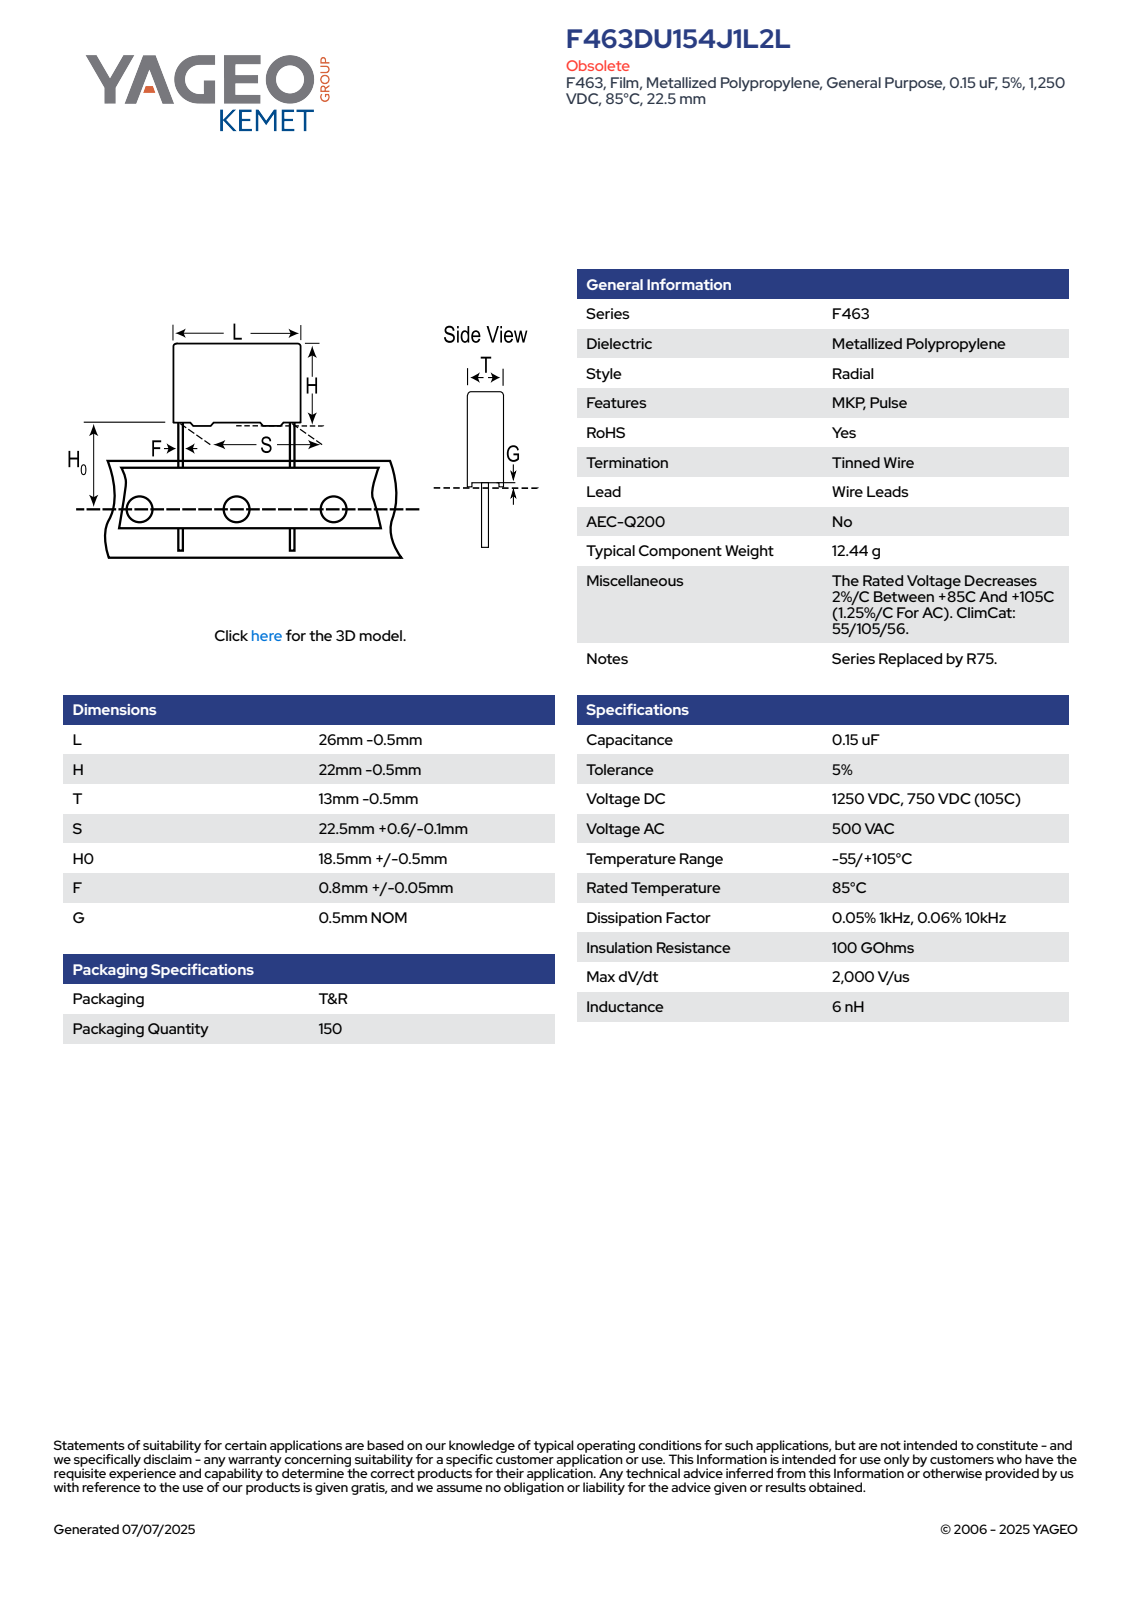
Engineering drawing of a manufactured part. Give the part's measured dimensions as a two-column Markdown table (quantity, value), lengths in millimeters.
| quantity | value |
| --- | --- |
| part name | CFR_RBG_26X22X13_L25.5H21.5T12.5S22.5H019F0.85G0.5 |
| STEP written by | SolidWorks 2014 (AUTOMOTIVE_DESIGN) |
| units | millimeters |
| bodies | 4 solids, 89 faces (81 planar, 8 cylindrical, 0 other) |
| overall size | 40.5 × 25.5 × 12.51 |
| volume | 6 718 mm³ |
| surface area | 2 410 mm² |
| round bosses / shafts (diameter × count) | 0.85 × 2 |
| partial cylindrical surfaces (radius × count) | 0.5 × 4 |
| main face-to-face distances | 12.5, 21, 25.5, 12.51, 0.5, 21.5, 0.71, 11.79, 0.72, 11.08 |
